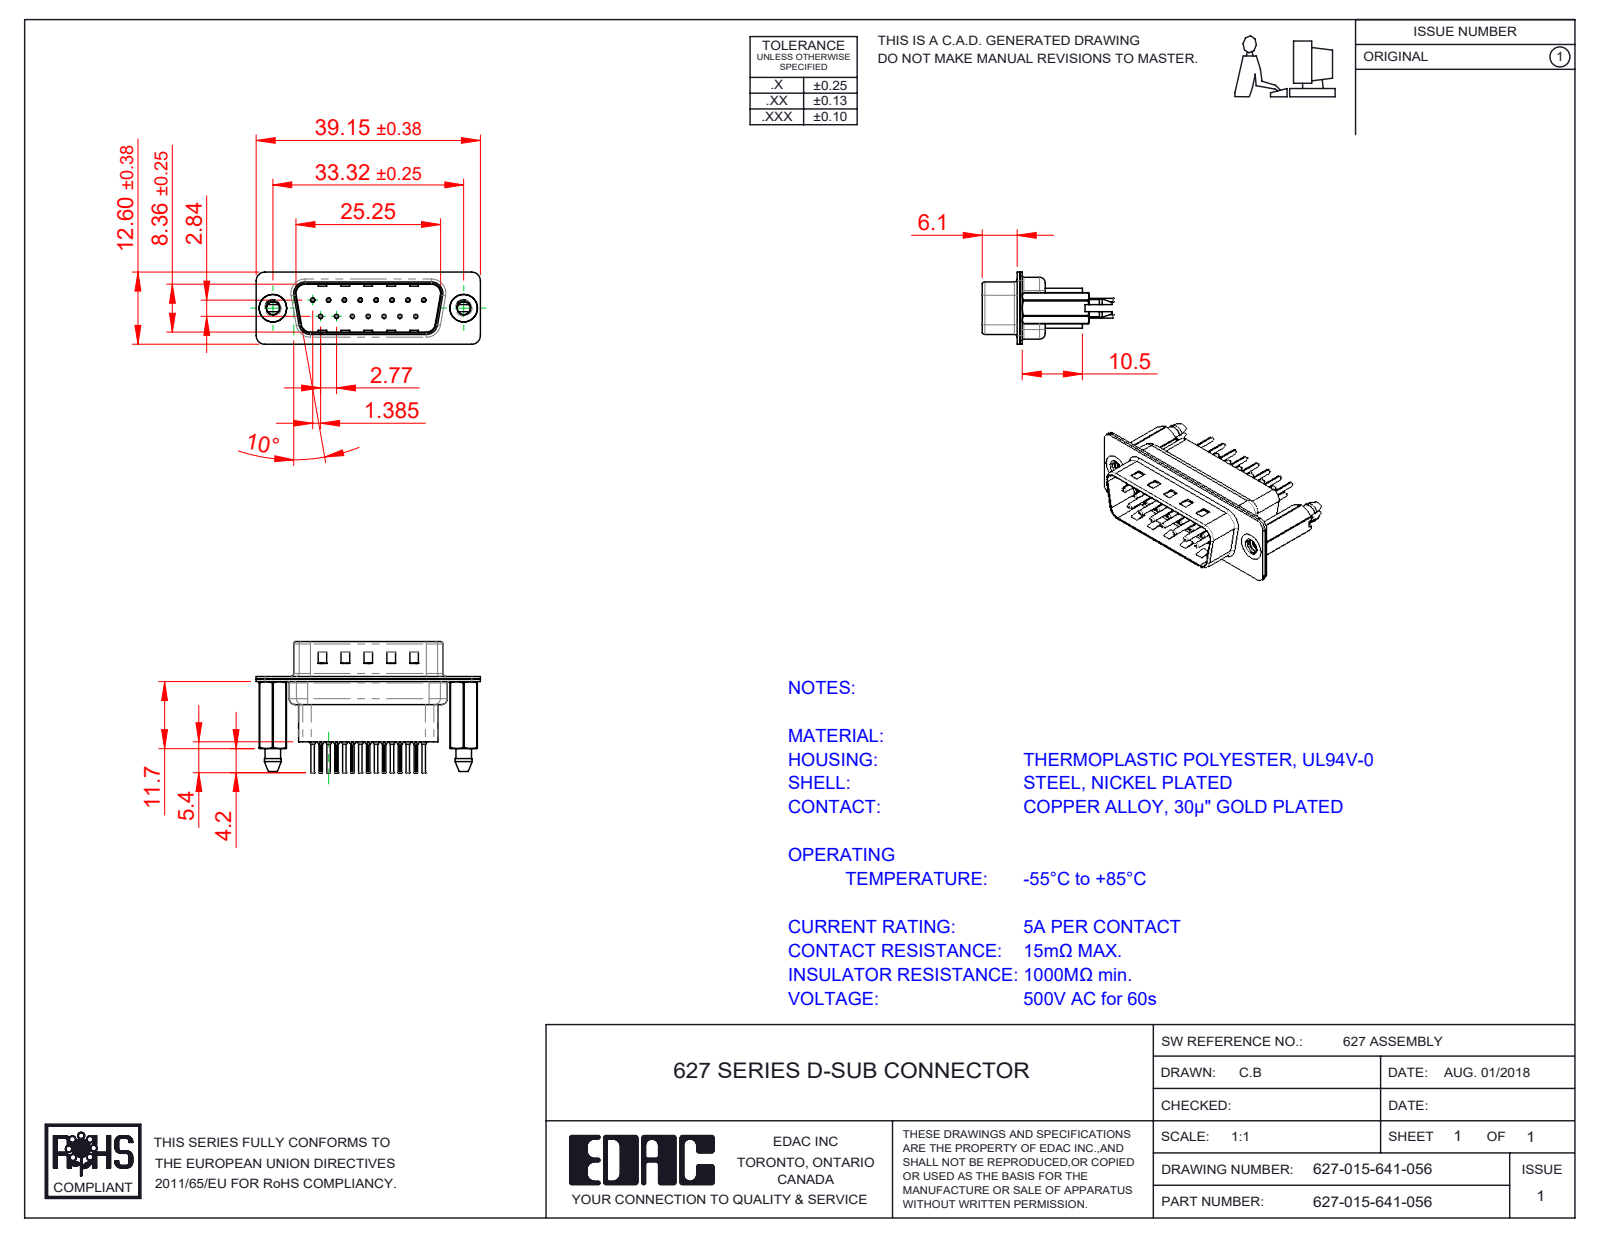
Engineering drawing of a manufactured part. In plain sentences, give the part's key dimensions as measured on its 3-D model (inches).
The part is named "627 Contact Row 2_41; 627 Shell Front_15 Contacts; 627 Shell Rear_15 Contacts; 627 4-40 Threaded Boardlock_HP41 (+3 more)". Its 3-D file was written by "SolidWorks 2020 (CONFIG_CONTROL_DESIGN)". It is 20 solids with 1918 faces: 531 planar, 754 cylindrical and 633 other. Overall it measures 1.541 by 0.898 by 0.496 inches. Its volume is 0.172 cubic inches and its surface area 11.35 square inches. Round holes: 15 of diameter 0.008, 15 of diameter 0.014, 15 of diameter 0.043, 15 of diameter 0.063, 2 of diameter 0.089, 2 of diameter 0.157, 2 of diameter 0.189. Round bosses or shafts: 15 of diameter 0.079, 15 of diameter 0.059, 15 of diameter 0.03, 15 of diameter 0.024, 2 of diameter 0.193. Partial cylindrical surfaces (rounded edges, fillets, slot ends): 30 of radius 0.004, 18 of radius 0.059, 12 of radius 0.079, 10 of radius 0.063, 8 of radius 0.02, 4 of radius 0.01, 4 of radius 0.024, 4 of radius 0.026. The main face-to-face distances are 0.016, 0.018, 0.035, 0.032, 0.377, 0.059, 0.027, 0.302, 0.055, 0.043. The hole center spacings are 0.124, 0.109, 0.218, 0.327, 0.436, 0.198, 0.198, 0.294.
